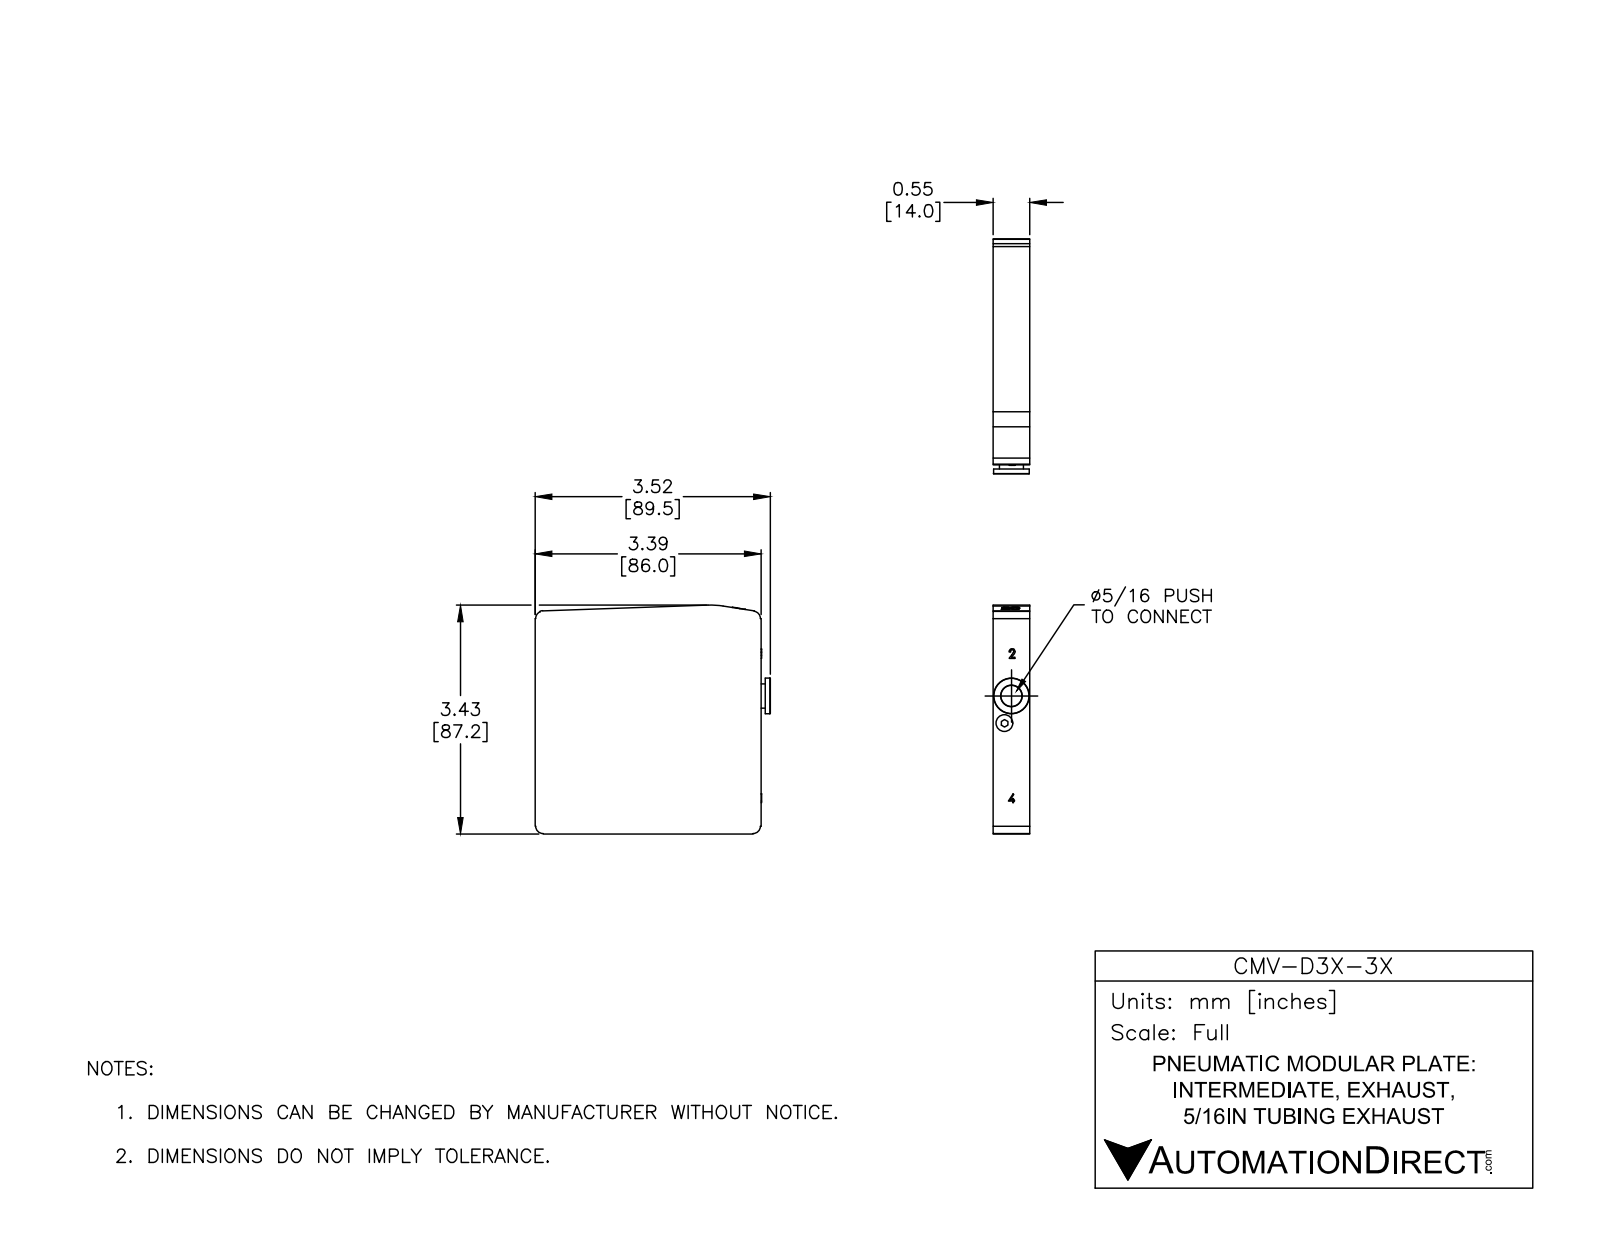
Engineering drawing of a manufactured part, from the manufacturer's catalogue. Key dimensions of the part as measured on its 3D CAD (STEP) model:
Part name (STEP PRODUCT): CMV-D3X-3X
STEP written by: SolidWorks 2017 (AUTOMOTIVE_DESIGN)
Units: millimetres
Bodies: 1 solid, 126 faces (62 planar, 60 cylindrical, 4 other)
Overall size (bounding box): 89.5 × 87.22 × 14
Volume: 103 641 mm³ · Surface area: 19 938 mm²
Round holes (diameter × count): ⌀6.4 ×1, ⌀8 ×1
Round bosses / shafts (diameter × count): ⌀13.6 ×1, ⌀9.2 ×1
Partial cylindrical surfaces — rounded edges, fillets, slot ends (radius × count): R2.8 ×4, R0.98 ×2, R1.34 ×2, R1.44 ×2, R1.51 ×2, R2.15 ×2, R2.21 ×2, R3.46 ×2
Main face-to-face distances: 14, 86, 89.5, 3.5, 1.6, 87.6, 1.9, 85.8, 2.5, 1.8
Hole centre spacings: 10.72
